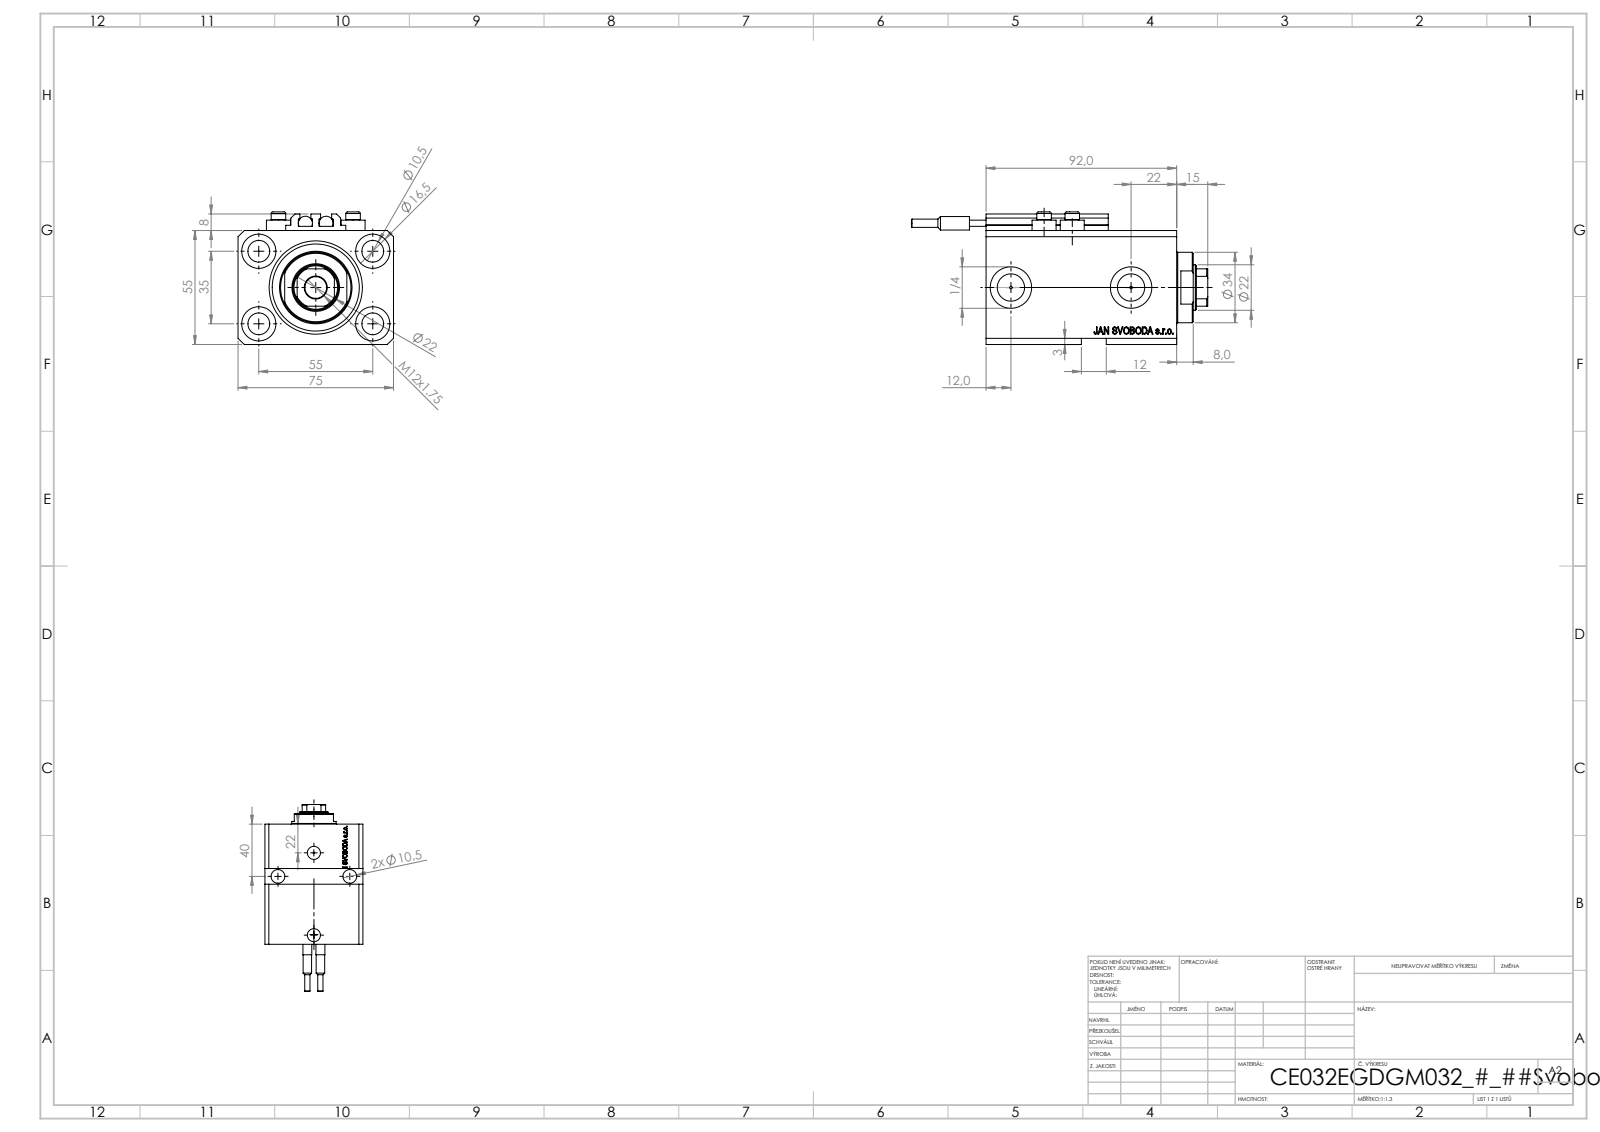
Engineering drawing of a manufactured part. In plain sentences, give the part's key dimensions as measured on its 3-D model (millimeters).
The part is named "SWITCH_V250CE; ALLEN BOLT V250CE; V250CE_VC_E; V250CE_C_VCP (+1 more)". Its 3-D file was written by "SolidWorks 2019 (CONFIG_CONTROL_DESIGN)". It is 10 solids with 1132 faces: 550 planar, 150 cylindrical and 432 other. Overall it measures 143 by 75 by 64 millimeters. Its volume is 325 400 cubic millimeters and its surface area 86 226 square millimeters. Round holes: 7 of diameter 10.5, 4 of diameter 1.25, 4 of diameter 4, 4 of diameter 16.5, 2 of diameter 10, 2 of diameter 13.16, 2 of diameter 20, 1 of diameter 22, 1 of diameter 32, 1 of diameter 45. Round bosses or shafts: 4 of diameter 11.6, 4 of diameter 7, 2 of diameter 6.8, 2 of diameter 6.5, 2 of diameter 4, 1 of diameter 34. Partial cylindrical surfaces (rounded edges, fillets, slot ends): 10 of radius 0.2, 1 of radius 10.5. The main face-to-face distances are 55, 75, 3, 15, 92, 77, 9.9, 57, 67.1, 82.1. The hole center spacings are 32.6, 55, 13.6, 14.09, 25.81, 27.26, 27.66, 32.87.
